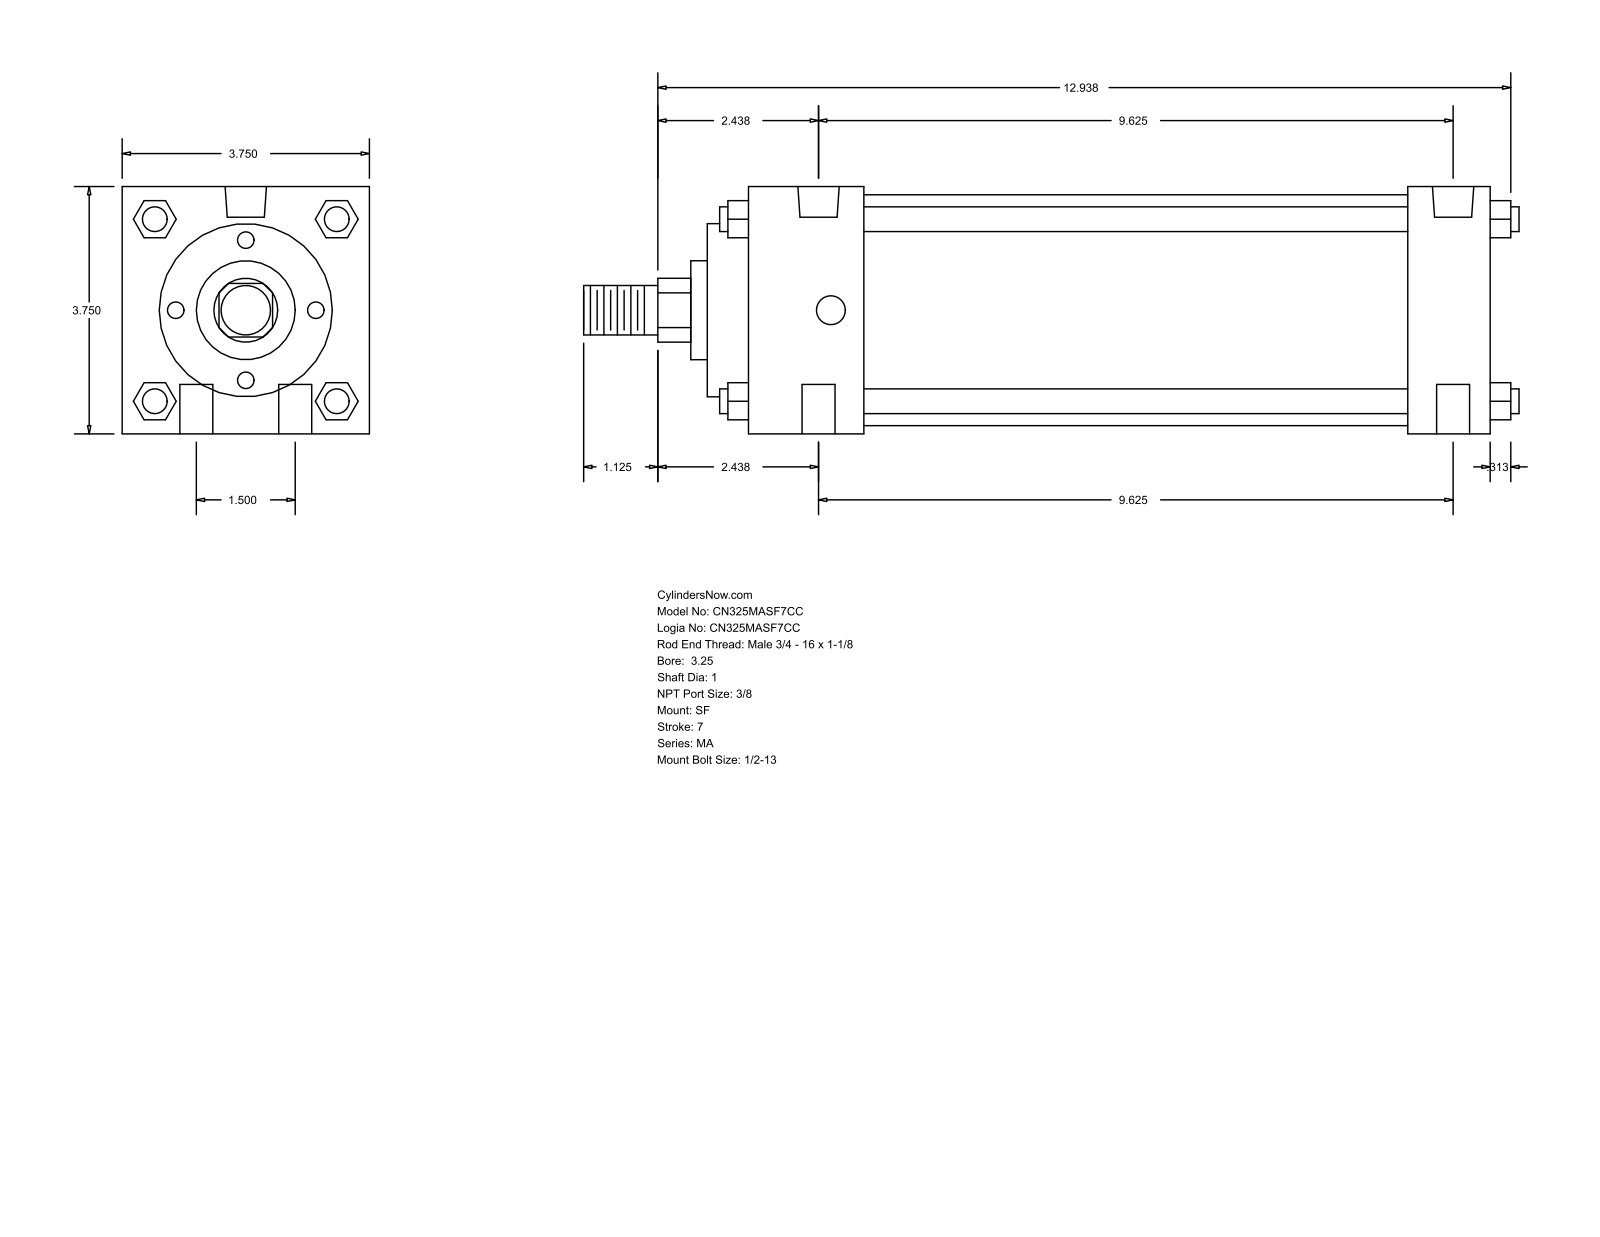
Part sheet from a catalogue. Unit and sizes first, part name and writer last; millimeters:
Units: millimetres
Overall size (bounding box): 360.36 × 95.25 × 95.25
Round holes (diameter × count): ⌀12.7 ×4, ⌀11.11 ×2, ⌀15.93 ×2
Round bosses / shafts (diameter × count): ⌀9.53 ×4, ⌀88.9 ×1, ⌀66.67 ×1, ⌀38.1 ×1, ⌀25.4 ×1, ⌀19.05 ×1
Partial cylindrical surfaces — rounded edges, fillets, slot ends (radius × count): R12.29 ×1
Main face-to-face distances: 95.24, 285.76, 254.01, 31.75, 44.46, 209.55, 241.3, 15.87, 60.33, 269.88
Hole centre spacings: 19.05, 245.22, 244.48, 38.1, 247.43, 234.95
Bodies: 0 solids, 126 faces (95 planar, 31 cylindrical, 0 other)
Part name (STEP PRODUCT): MA_SF__0325_1
STEP written by: GSSL Pune (CONFIG_CONTROL_DESIGN)
